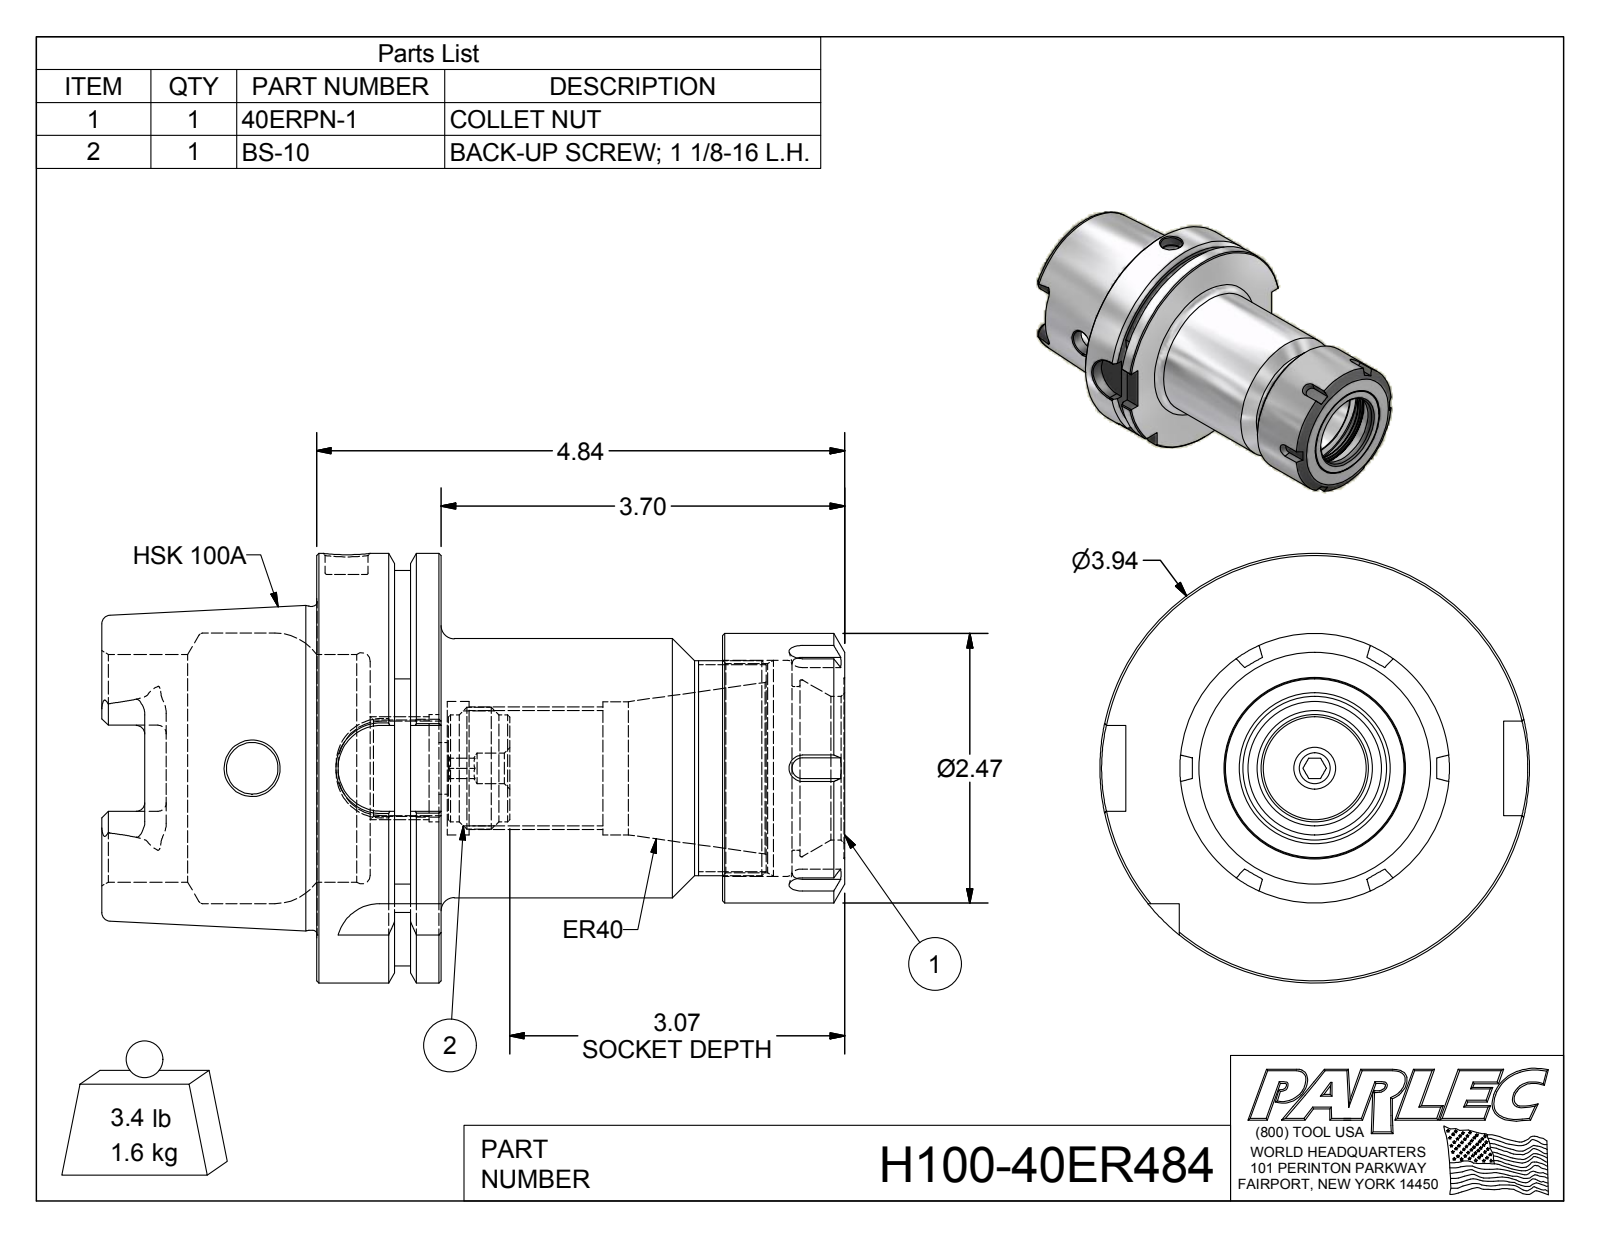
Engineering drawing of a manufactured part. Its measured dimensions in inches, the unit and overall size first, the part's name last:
Units: inches
Overall size (bounding box): 6.809 × 3.937 × 3.937
Round holes (diameter × count): ⌀0.472 ×2, ⌀0.22 ×1, ⌀0.28 ×1, ⌀0.394 ×1, ⌀0.881 ×1, ⌀0.985 ×1, ⌀1.057 ×1, ⌀1.22 ×1, ⌀1.225 ×1, ⌀1.318 ×1, ⌀1.5 ×1, ⌀1.62 ×1
Round bosses / shafts (diameter × count): ⌀3.937 ×1, ⌀2.967 ×1, ⌀2.47 ×1, ⌀2.375 ×1, ⌀1.969 ×1, ⌀1.118 ×1, ⌀0.98 ×1
Partial cylindrical surfaces — rounded edges, fillets, slot ends (radius × count): R0.079 ×6, R0.192 ×4, R0.394 ×4, R1.811 ×1
Main face-to-face distances: 1.142, 0.492, 0.65, 4.84, 4.348, 3.698, 3.72, 3.228, 2.578, 1.12
Volume: 27.14 in³ · Surface area: 133.6 in²
Bodies: 3 solids, 198 faces (76 planar, 47 cylindrical, 75 other)
Part name (STEP PRODUCT): H100-40ER484; H100-40ER5; H100-40ER5-1; BS-10 (+1 more)
STEP written by: Autodesk Inventor 2012 (AUTOMOTIVE_DESIGN)
